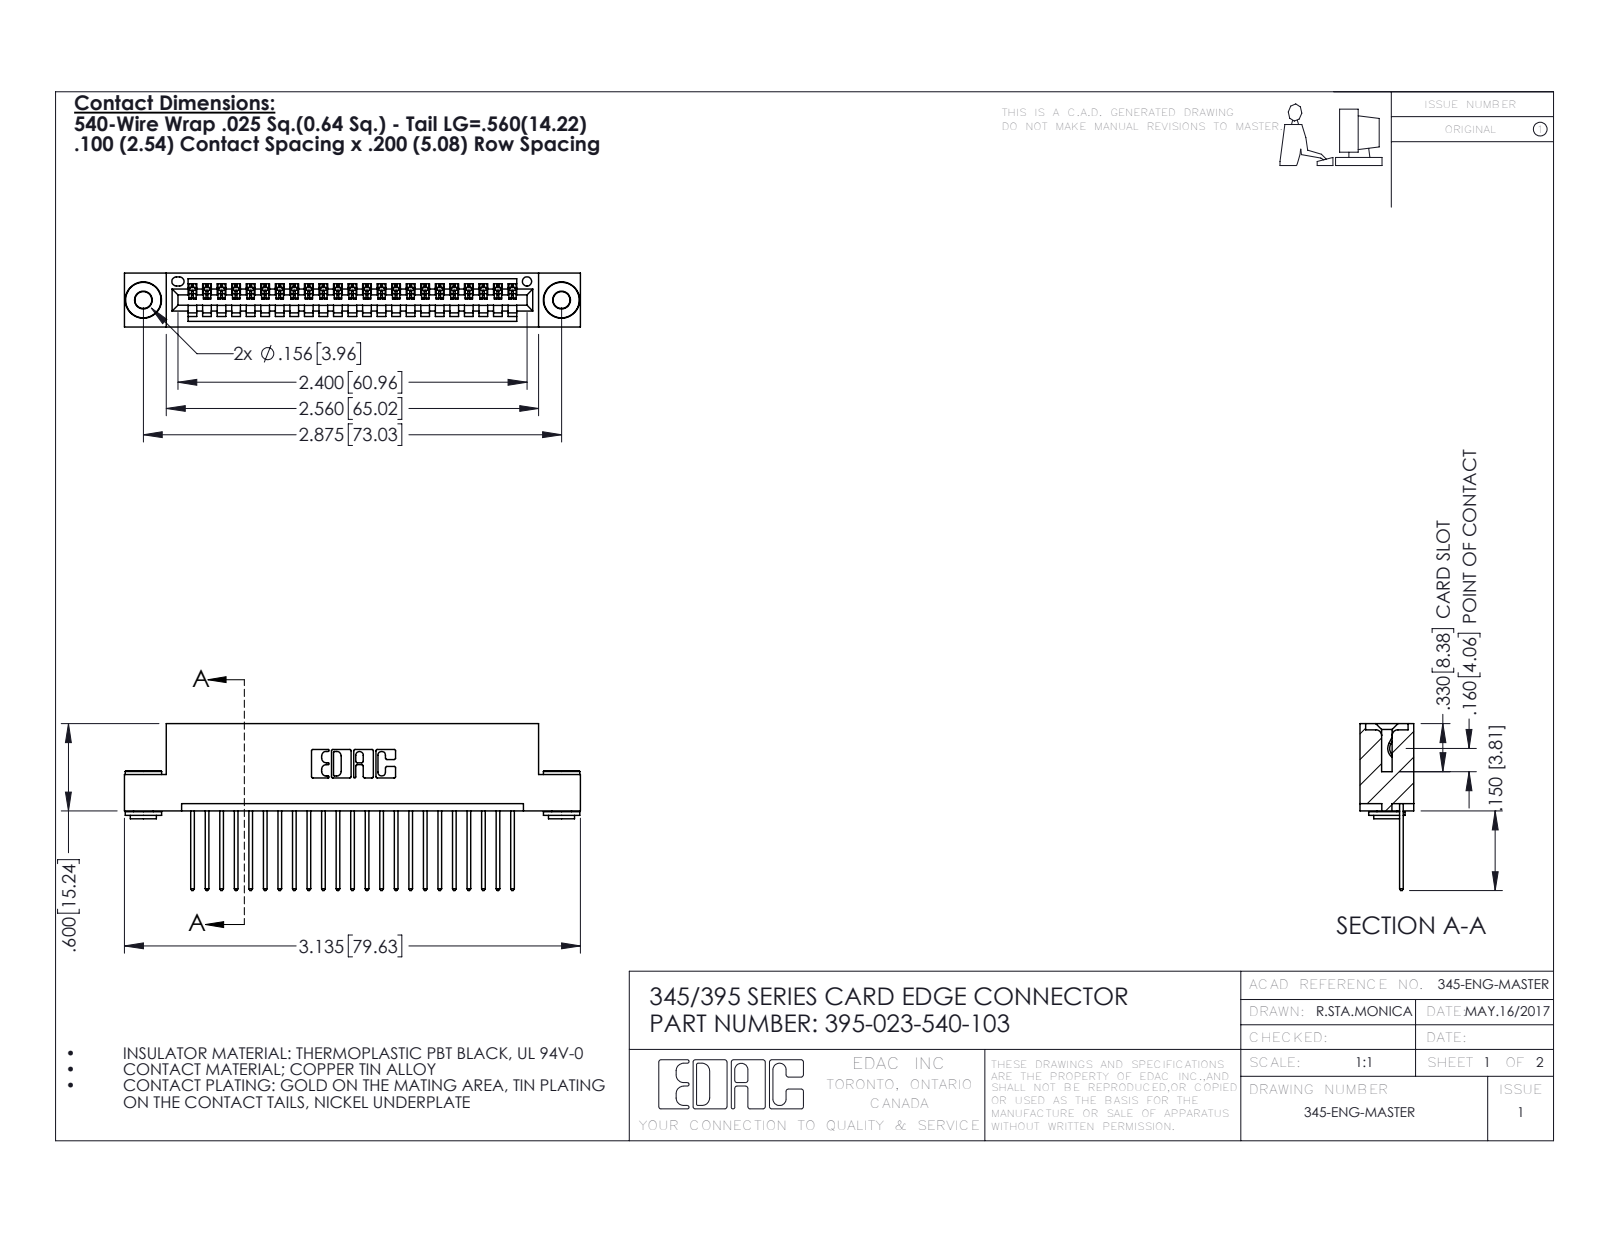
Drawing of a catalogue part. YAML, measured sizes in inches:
part_name: "345-250-002_345-250-002-102; 345 Part_Flush Mounting Lugs - 0.156 Dia-TH; 345-292-001_345-293-140; 395-023-540-103"
step_written_by: "SolidWorks 2016 (CONFIG_CONTROL_DESIGN)"
units: inches
bodies: {solids: 26, faces: 1498, planar: 1010, cylindrical: 480, other: 8}
overall_size: [3.135, 1.147, 0.37]
volume: 0.455
surface_area: 15.64
round_holes:
  - {diameter: 0.116, count: 2}
  - {diameter: 0.156, count: 2}
  - {diameter: 0.064, count: 1}
round_bosses_or_shafts:
  - {diameter: 0.25, count: 2}
  - {diameter: 0.18, count: 2}
  - {diameter: 0.136, count: 2}
partial_cylinders:
  - {radius: 0.006, count: 46}
  - {radius: 0.01, count: 46}
  - {radius: 0.01, count: 22}
  - {radius: 0.007, count: 6}
  - {radius: 0.031, count: 6}
  - {radius: 0.026, count: 3}
  - {radius: 0.031, count: 2}
  - {radius: 0.04, count: 2}
face_to_face_distances: [0.072, 0.298, 0.2, 0.37, 0.025, 0.098, 0.272, 0.225, 0.149, 0.072]
hole_center_spacings: [0.27, 2.641, 2.875]
